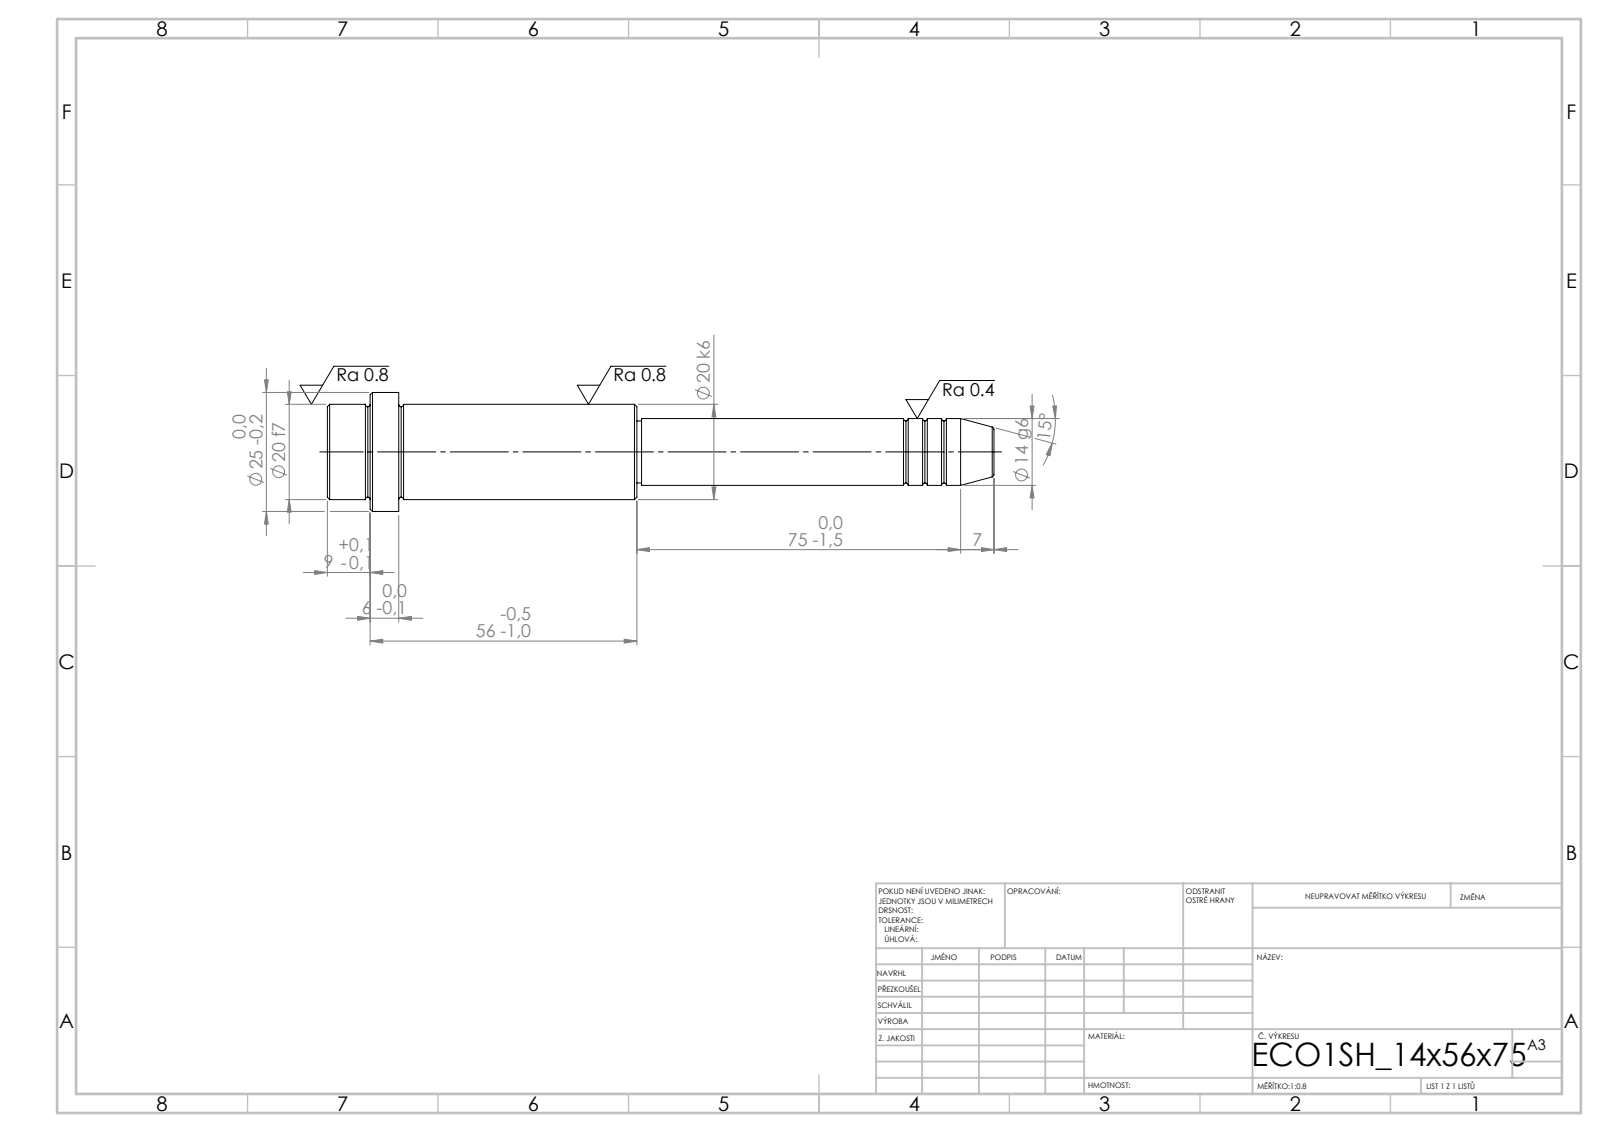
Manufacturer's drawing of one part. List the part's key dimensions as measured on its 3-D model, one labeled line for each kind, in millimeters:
STEP written by: SolidWorks 2019 (CONFIG_CONTROL_DESIGN)
Units: millimetres
Bodies: 1 solid, 52 faces (6 planar, 16 cylindrical, 30 other)
Overall size (bounding box): 140 × 25 × 25
Volume: 32 617 mm³ · Surface area: 8 462 mm²
Round bosses / shafts (diameter × count): ⌀25 ×1, ⌀20 ×1, ⌀14 ×1, ⌀13 ×1
Main face-to-face distances: 15, 50, 65, 56, 6, 9, 75, 125, 131, 140
